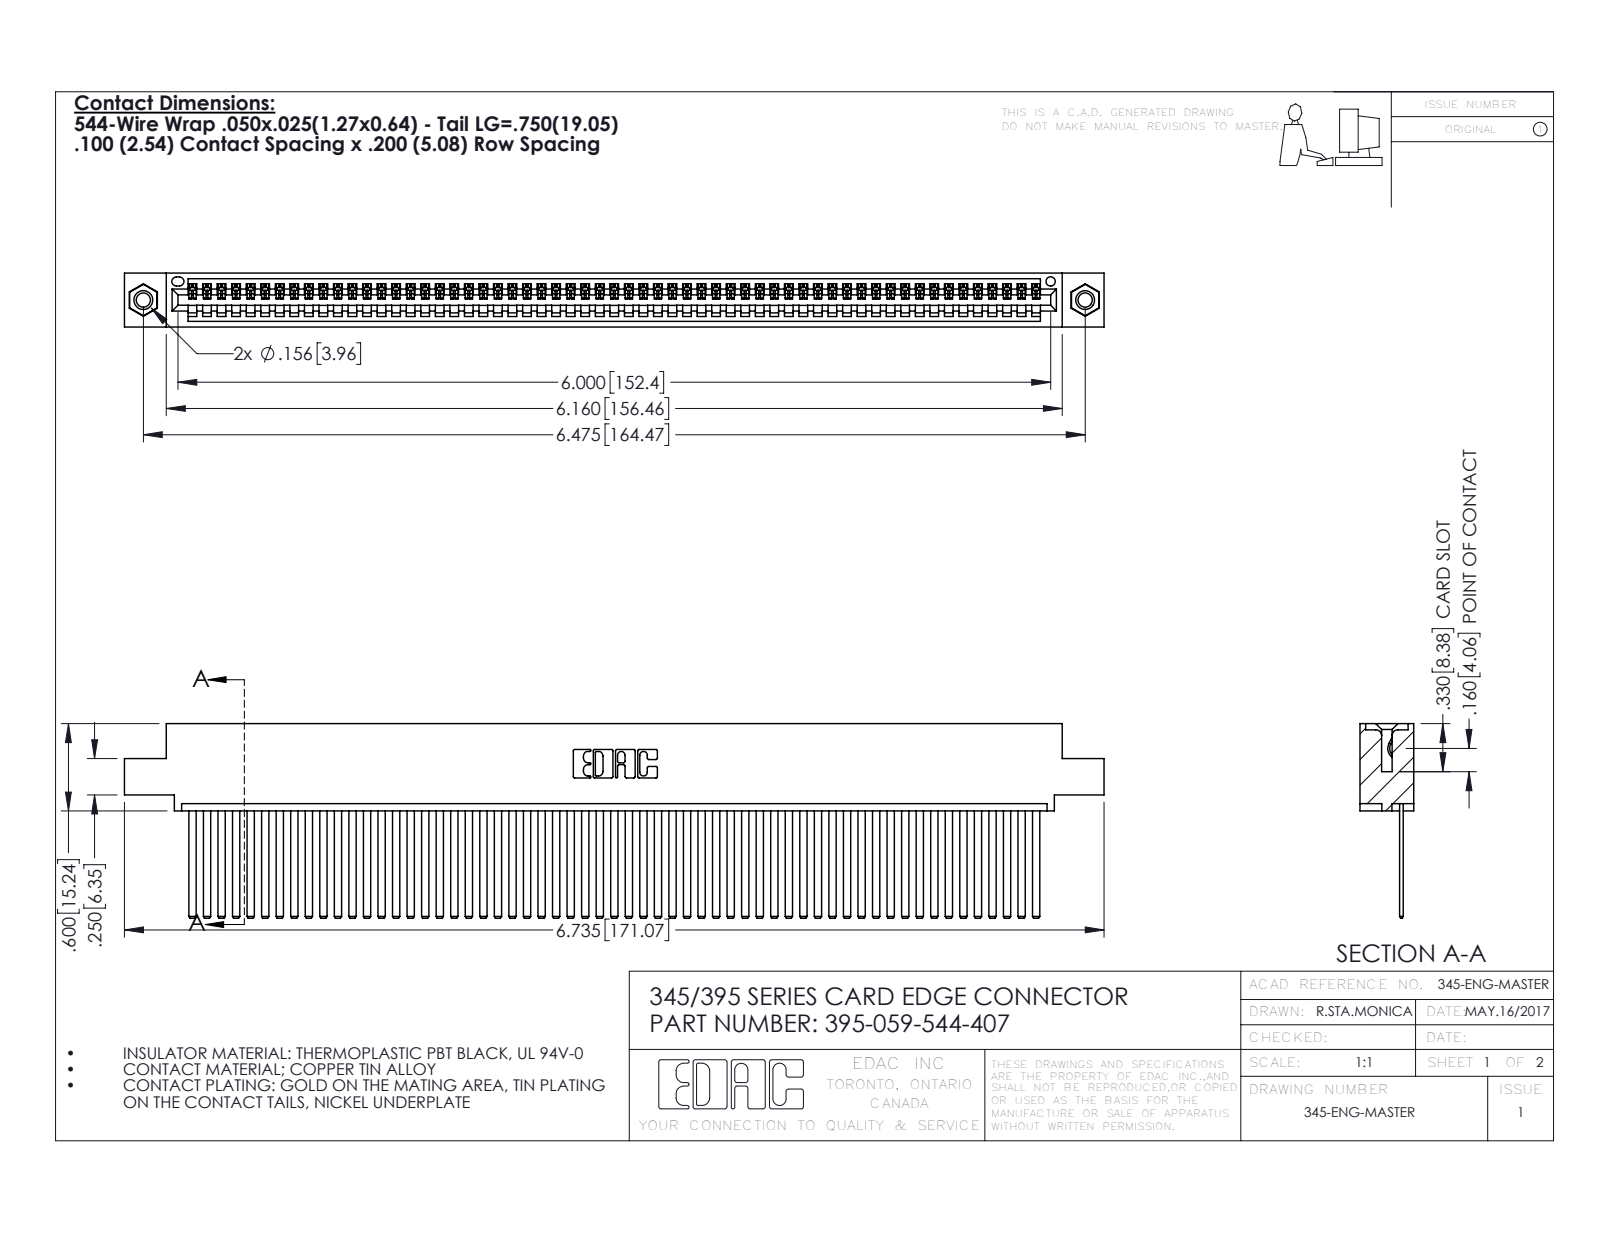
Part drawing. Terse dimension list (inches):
name: 345 Part_0.110 Offset - 0.156 Dia-TI; 345-292-001_345-293-144; 395-059-544-407; 345-250-001_345-250-005-103
written by: SolidWorks 2016 (CONFIG_CONTROL_DESIGN)
unit: in
bodies: 62 solids, 3258 faces (2240 planar, 1002 cylindrical, 16 other)
size: 6.735 × 1.337 × 0.37
volume: 1.036 in³; area: 38.7 in²
holes: 2× ⌀0.098, 2× ⌀0.125, 2× ⌀0.156, 1× ⌀0.064
bosses: 2× ⌀0.155
rounds: 118× R0.006, 22× R0.01, 6× R0.007, 6× R0.031, 3× R0.026, 2× R0.031, 2× R0.04, 1× R0.014
face distances: 0.072, 0.298, 0.025, 0.098, 0.272, 0.37, 0.2, 0.225, 0.149, 0.072
hole spacings: 0.27, 6.239, 6.475
